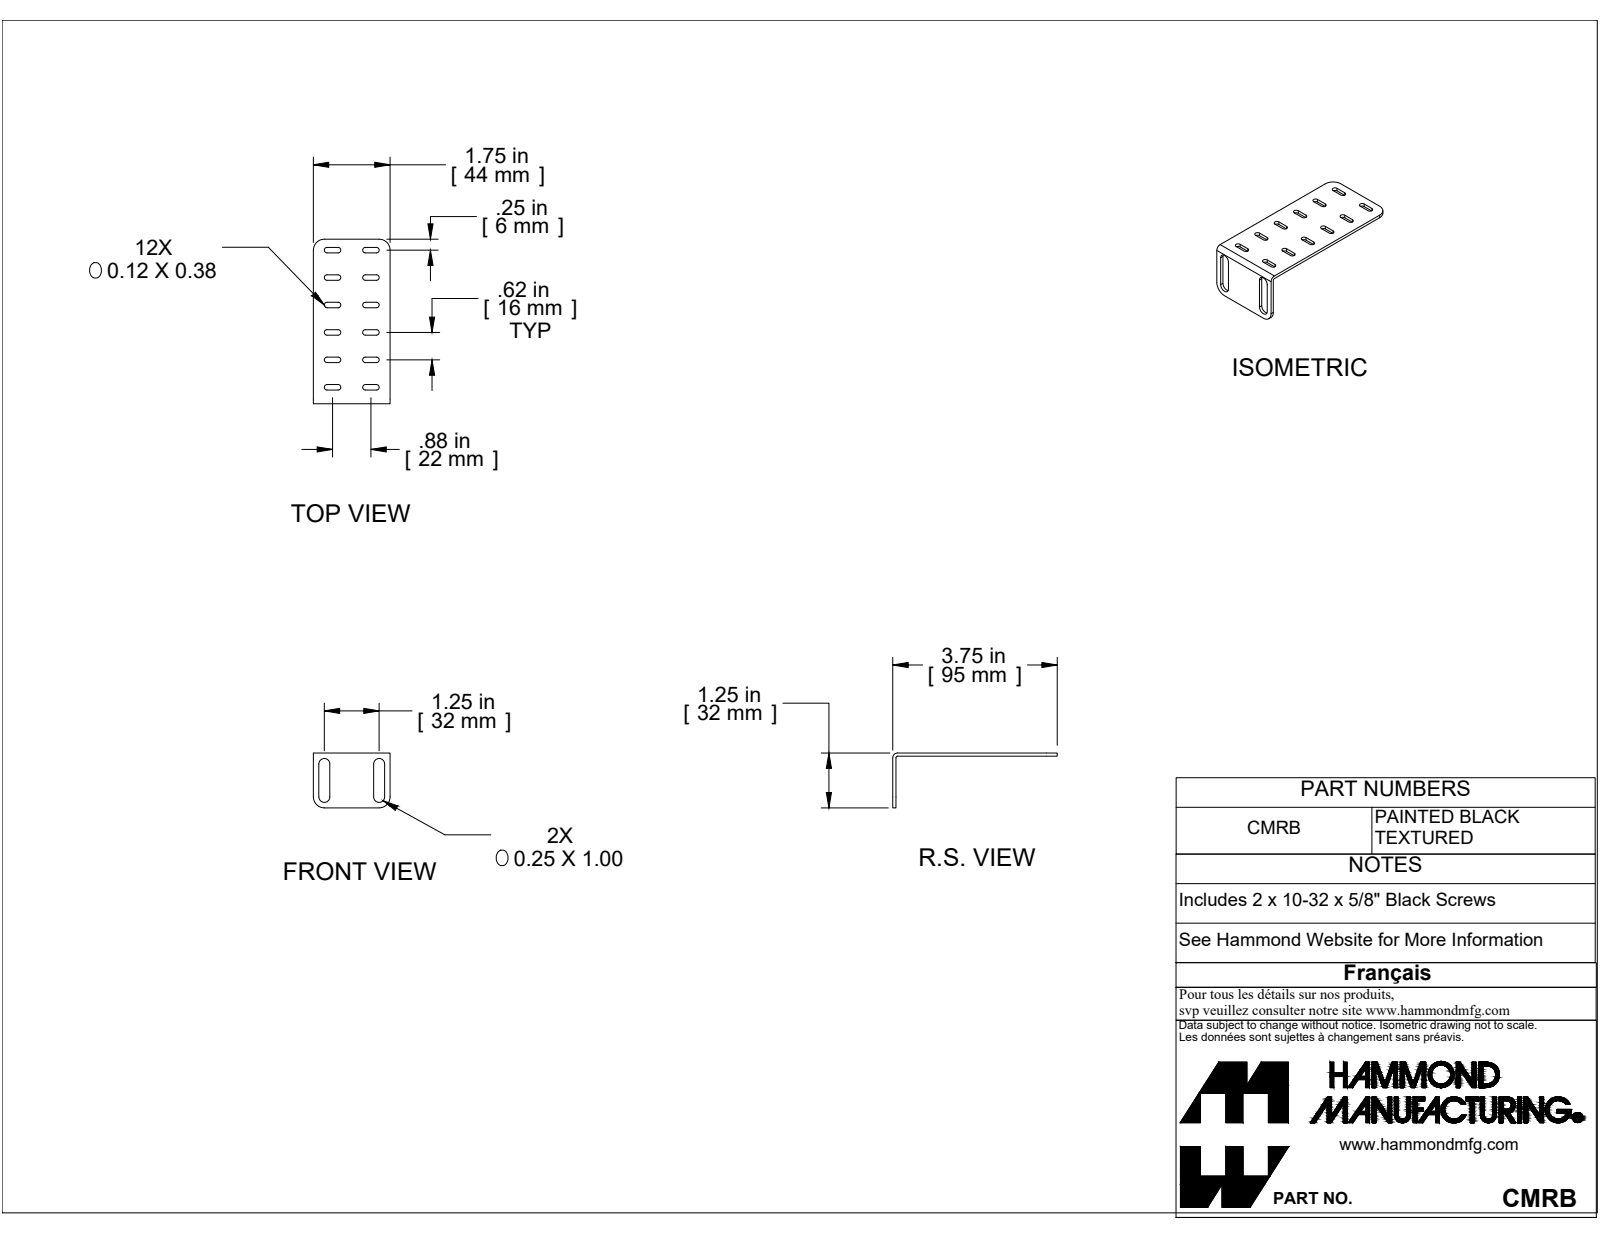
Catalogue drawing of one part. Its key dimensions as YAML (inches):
part_name: "CMRBK1"
step_written_by: "SolidWorks 2019 (AUTOMOTIVE_DESIGN)"
units: inches
bodies: {solids: 1, faces: 54, planar: 36, cylindrical: 18, other: 0}
overall_size: [3.5, 1.75, 1.25]
volume: 0.511
surface_area: 19.55
partial_cylinders:
  - {radius: 0.125, count: 6}
  - {radius: 0.029, count: 4}
  - {radius: 0.086, count: 4}
  - {radius: 0.25, count: 4}
face_to_face_distances: [0.057, 1.193, 1.25, 1.136, 3.443, 3.5, 3.386, 1, 0.375, 1.375]
